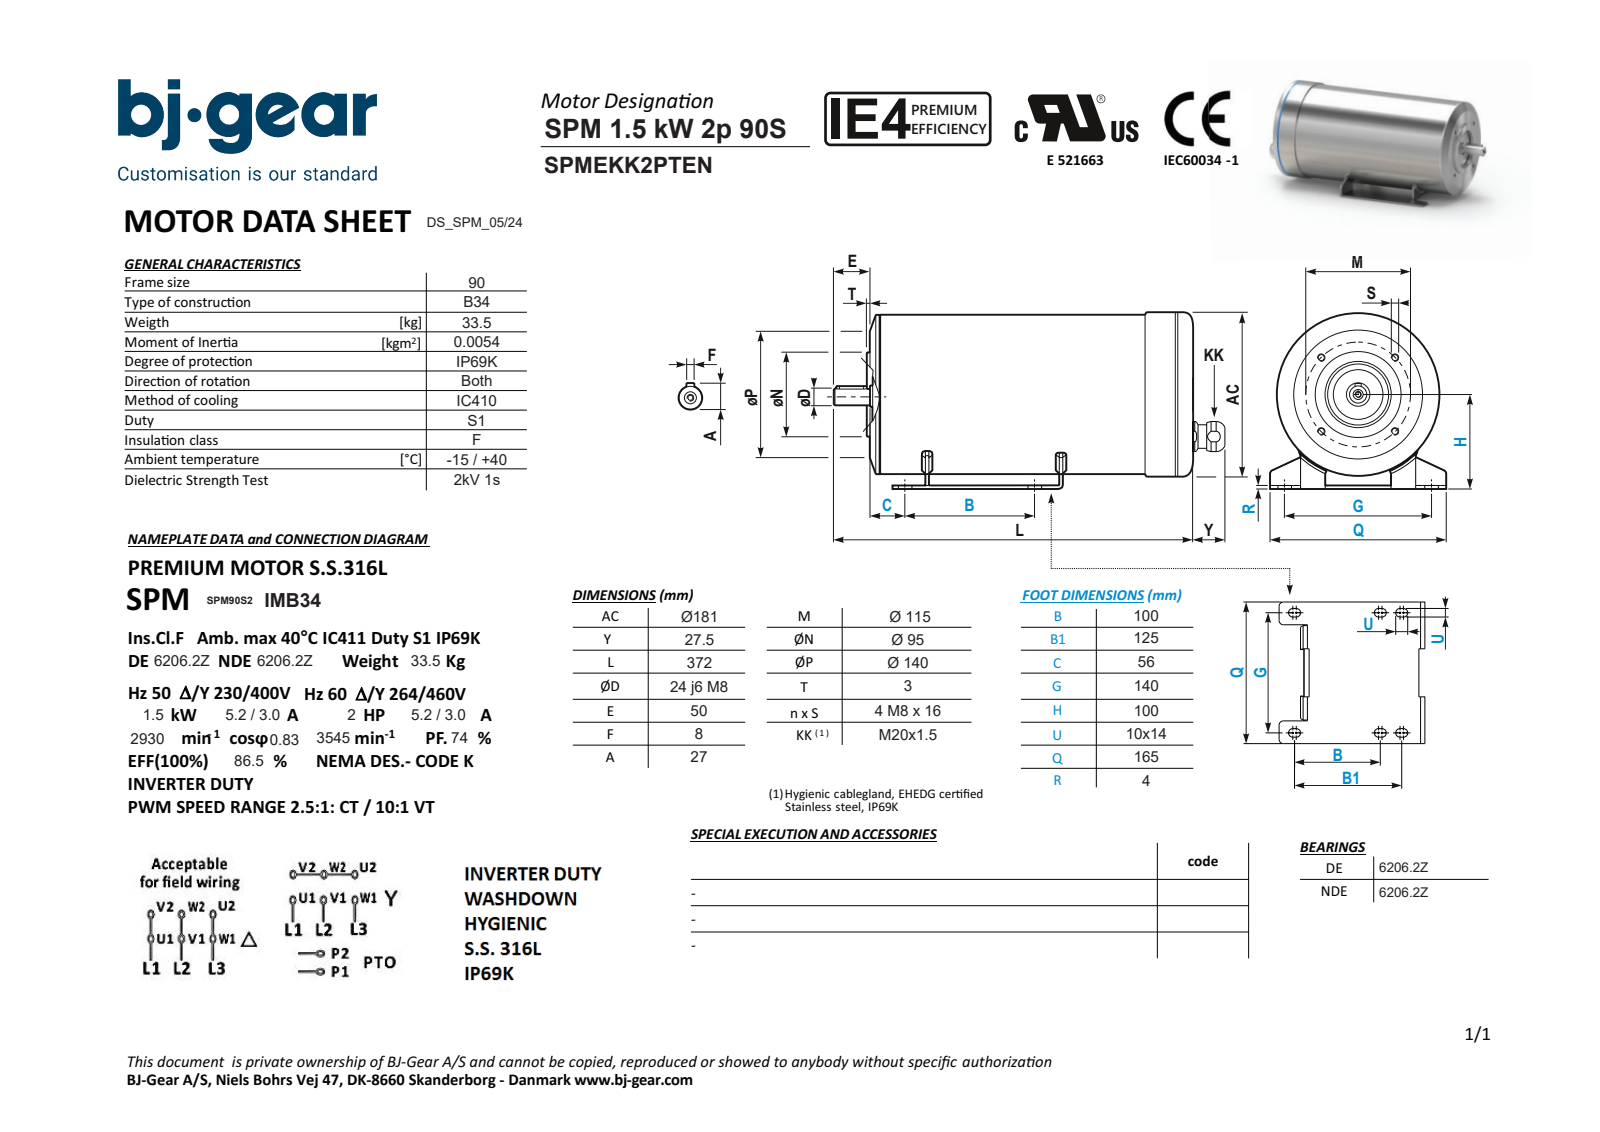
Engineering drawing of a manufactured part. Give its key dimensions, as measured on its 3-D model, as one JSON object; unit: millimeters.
{"part_name": "SPMEKK2PTENN4KSA1-N---NNN; SPMEKK2JTENN4KSA1-N---NNN; SPM909022", "step_written_by": "Solid Edge (AUTOMOTIVE_DESIGN)", "units": "millimeters", "bodies": {"solids": 2, "faces": 165, "planar": 70, "cylindrical": 70, "other": 25}, "overall_size": [399.5, 190.5, 181], "volume_mm3": 8119000, "surface_area_mm2": 295459, "round_holes": [[6.65, 4], [4.92, 1], [7, 1], [8.4, 1], [13.4, 1], [85, 1]], "round_bosses_or_shafts": [[181, 1], [180.98, 1], [178, 1], [177.98, 1], [95, 1], [30, 1], [24, 1], [20, 1]], "partial_cylinders_radius": [[5, 18], [3, 6], [1, 4], [4, 2], [12.8, 1], [88.5, 1]], "face_to_face_distances": [4, 322, 6, 316, 204, 114, 118, 202, 208, 198], "hole_center_spacings": [57.5, 81.32, 43.11, 103.94, 115, 55]}
